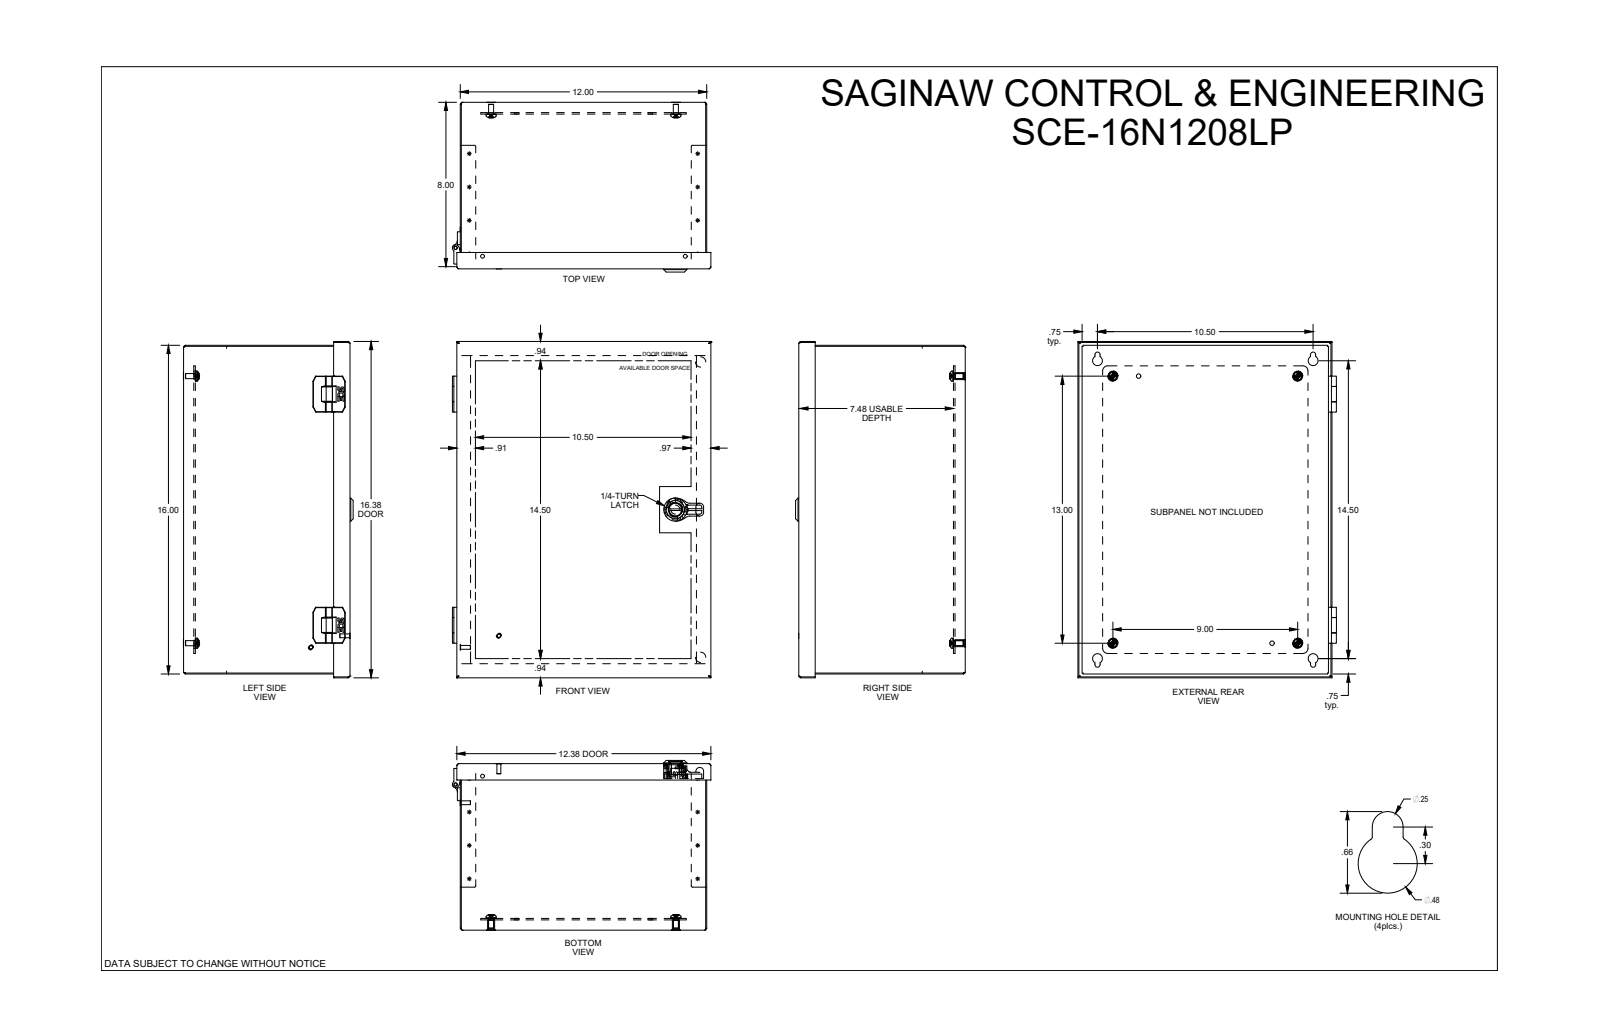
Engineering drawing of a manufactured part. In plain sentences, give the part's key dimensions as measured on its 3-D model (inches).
The part is named "SCE-16N1208LP". Its 3-D file was written by "SolidWorks 2019 (AUTOMOTIVE_DESIGN)". It is 31 solids with 1545 faces: 578 planar, 643 cylindrical and 324 other. Overall it measures 16.375 by 12.593 by 8.267 inches. Its volume is 66.41 cubic inches and its surface area 2 136 square inches. Round holes: 4 of diameter 0.17, 4 of diameter 0.25, 4 of diameter 0.281, 4 of diameter 0.329, 4 of diameter 0.343, 4 of diameter 0.48, 3 of diameter 0.193, 2 of diameter 0.187, 2 of diameter 0.218, 1 of diameter 0.158, 1 of diameter 0.44, 1 of diameter 0.635. Round bosses or shafts: 4 of diameter 0.492, 4 of diameter 0.479, 4 of diameter 0.341, 4 of diameter 0.248, 4 of diameter 0.237, 4 of diameter 0.16, 2 of diameter 0.5, 2 of diameter 0.323. Partial cylindrical surfaces (rounded edges, fillets, slot ends): 253 of radius 0.01, 95 of radius 0.02, 25 of radius 0.06, 24 of radius 0.015, 24 of radius 0.025, 6 of radius 0.055, 6 of radius 0.25, 4 of radius 0.125. The main face-to-face distances are 0.06, 8.047, 11.94, 7.987, 8.107, 15.94, 0.5, 0.44, 0.575, 0.515. The hole center spacings are 1.061, 1.089, 1.091, 9.779, 11.25, 13.77, 16.856, 11.25.
